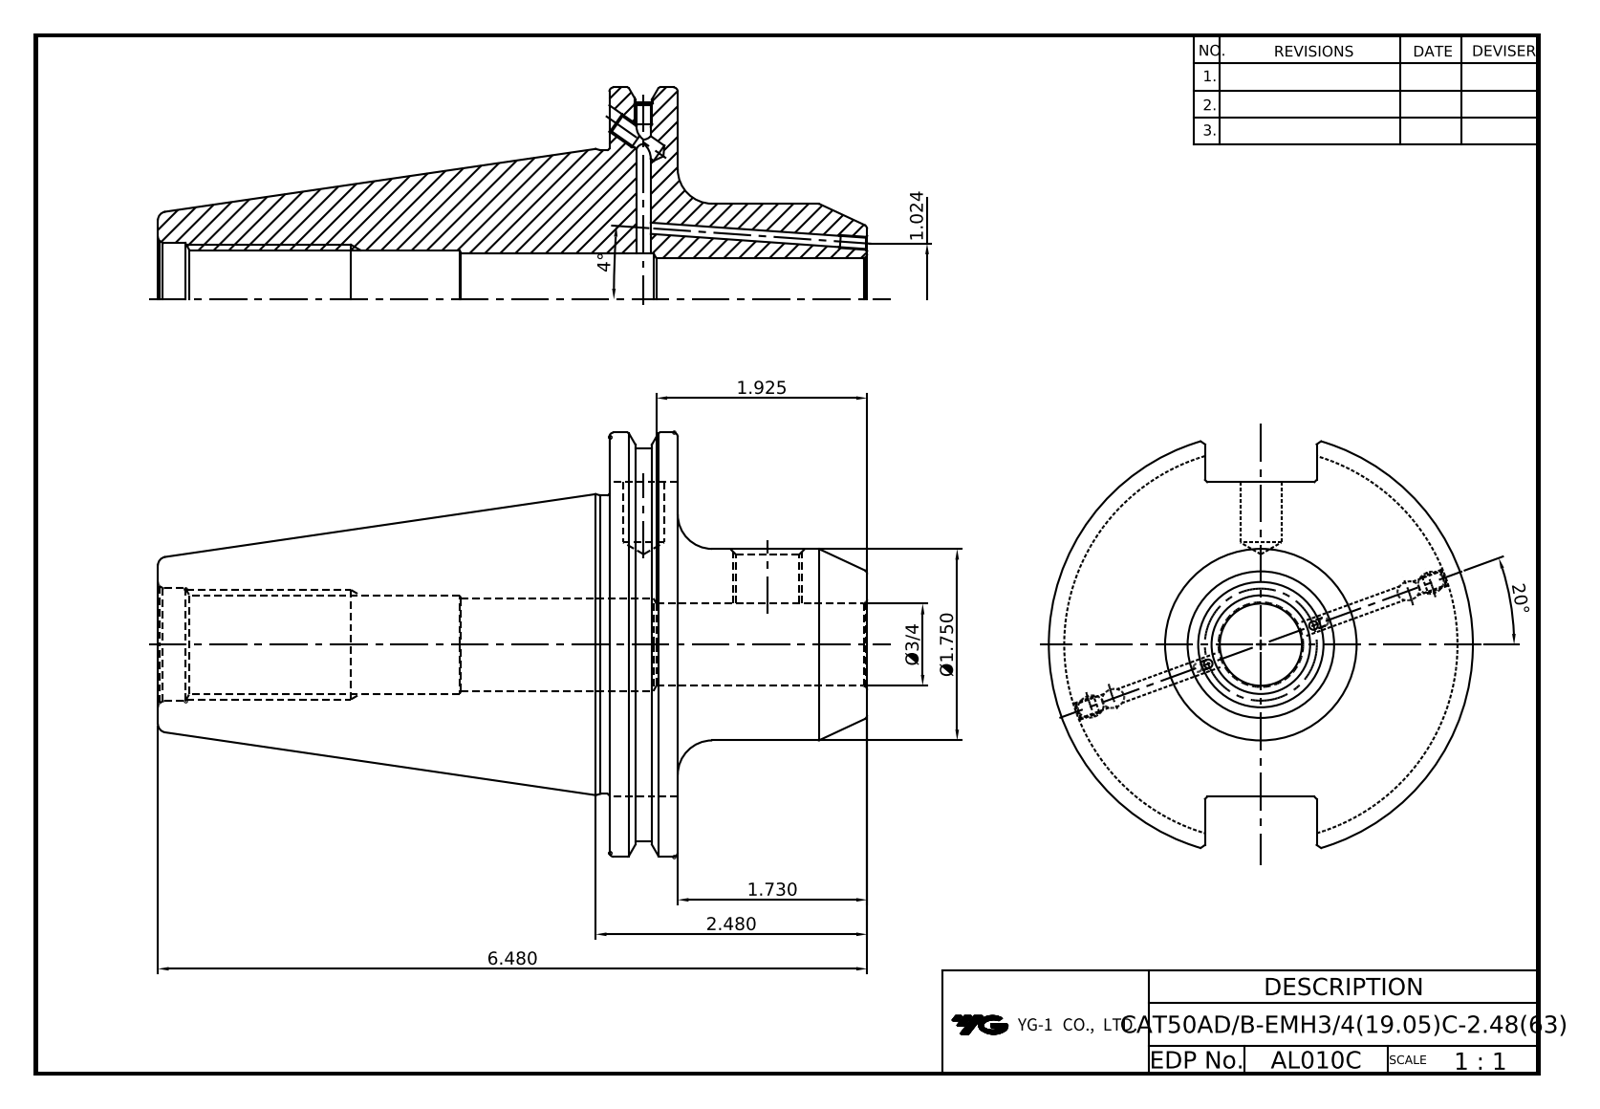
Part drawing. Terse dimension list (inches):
name: LO-CAT50ADB-EMH19.05C-63
written by: Autodesk Inventor 2025 (AUTOMOTIVE_DESIGN)
unit: in
bodies: 1 solid, 86 faces (36 planar, 27 cylindrical, 23 other)
size: 6.48 × 3.875 × 3.728
volume: 22.5 in³; area: 83.37 in²
holes: 2× ⌀0.097, 2× ⌀0.128, 2× ⌀0.163, 2× ⌀0.165, 2× ⌀0.197, 1× ⌀0.375, 1× ⌀0.565, 1× ⌀0.75, 1× ⌀0.865, 1× ⌀1.031
bosses: 1× ⌀3.875, 1× ⌀3.594, 1× ⌀2.726, 1× ⌀1.75
face distances: 0.625, 4.125, 4.75, 6.48, 2.356, 1.73, 2.875, 1.02, 4.513, 0.389
hole spacings: 1.133
